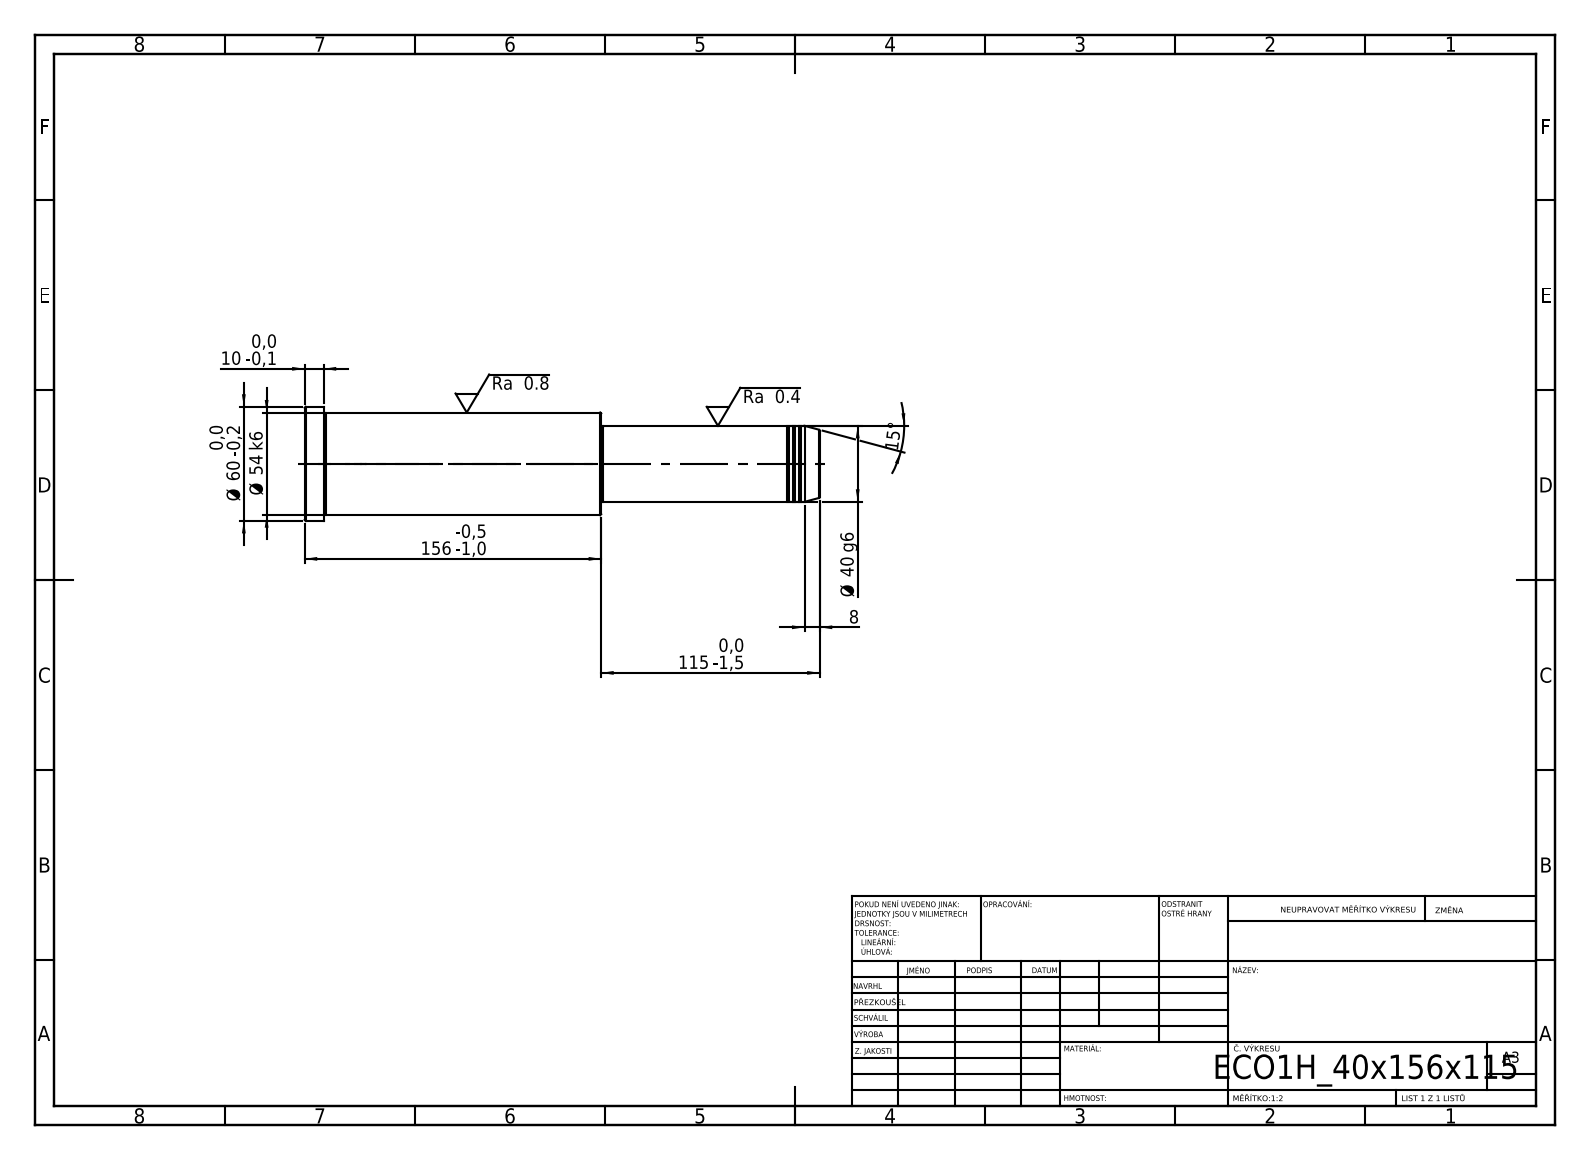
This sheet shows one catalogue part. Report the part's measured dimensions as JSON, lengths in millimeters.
{"step_written_by": "SolidWorks 2019 (CONFIG_CONTROL_DESIGN)", "units": "millimeters", "bodies": {"solids": 1, "faces": 43, "planar": 5, "cylindrical": 14, "other": 24}, "overall_size": [271, 60, 60], "volume_mm3": 505799, "surface_area_mm2": 46786, "round_bosses_or_shafts": [[60, 1], [54, 1], [40, 1], [39, 1]], "face_to_face_distances": [156, 115, 271, 261, 146, 10, 114, 1, 147, 157]}
